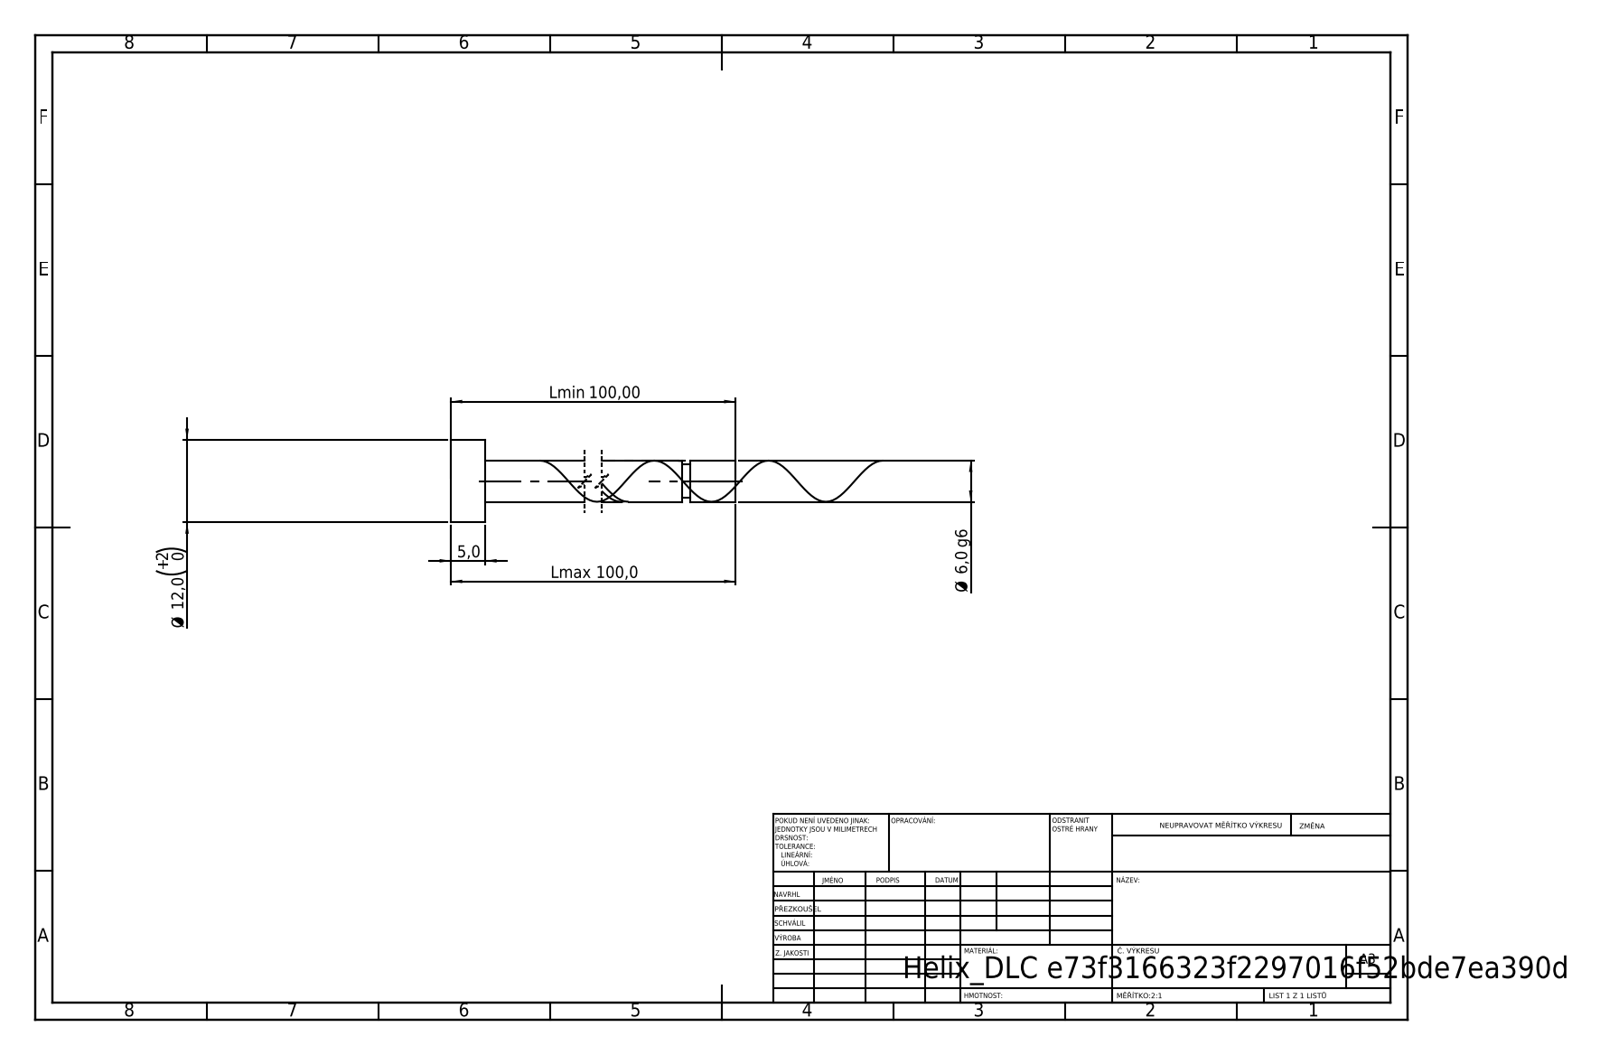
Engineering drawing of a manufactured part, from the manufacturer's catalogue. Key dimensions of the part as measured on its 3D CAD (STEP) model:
STEP written by: SolidWorks 2019 (CONFIG_CONTROL_DESIGN)
Units: millimetres
Bodies: 1 solid, 21 faces (6 planar, 14 cylindrical, 1 other)
Overall size (bounding box): 100 × 12 × 12
Volume: 3 212 mm³ · Surface area: 2 272 mm²
Round bosses / shafts (diameter × count): ⌀12 ×1, ⌀6 ×1, ⌀4.8 ×1
Main face-to-face distances: 5, 100, 95, 93.43, 88.43, 6.57, 92.23, 87.23, 1.2, 7.77
